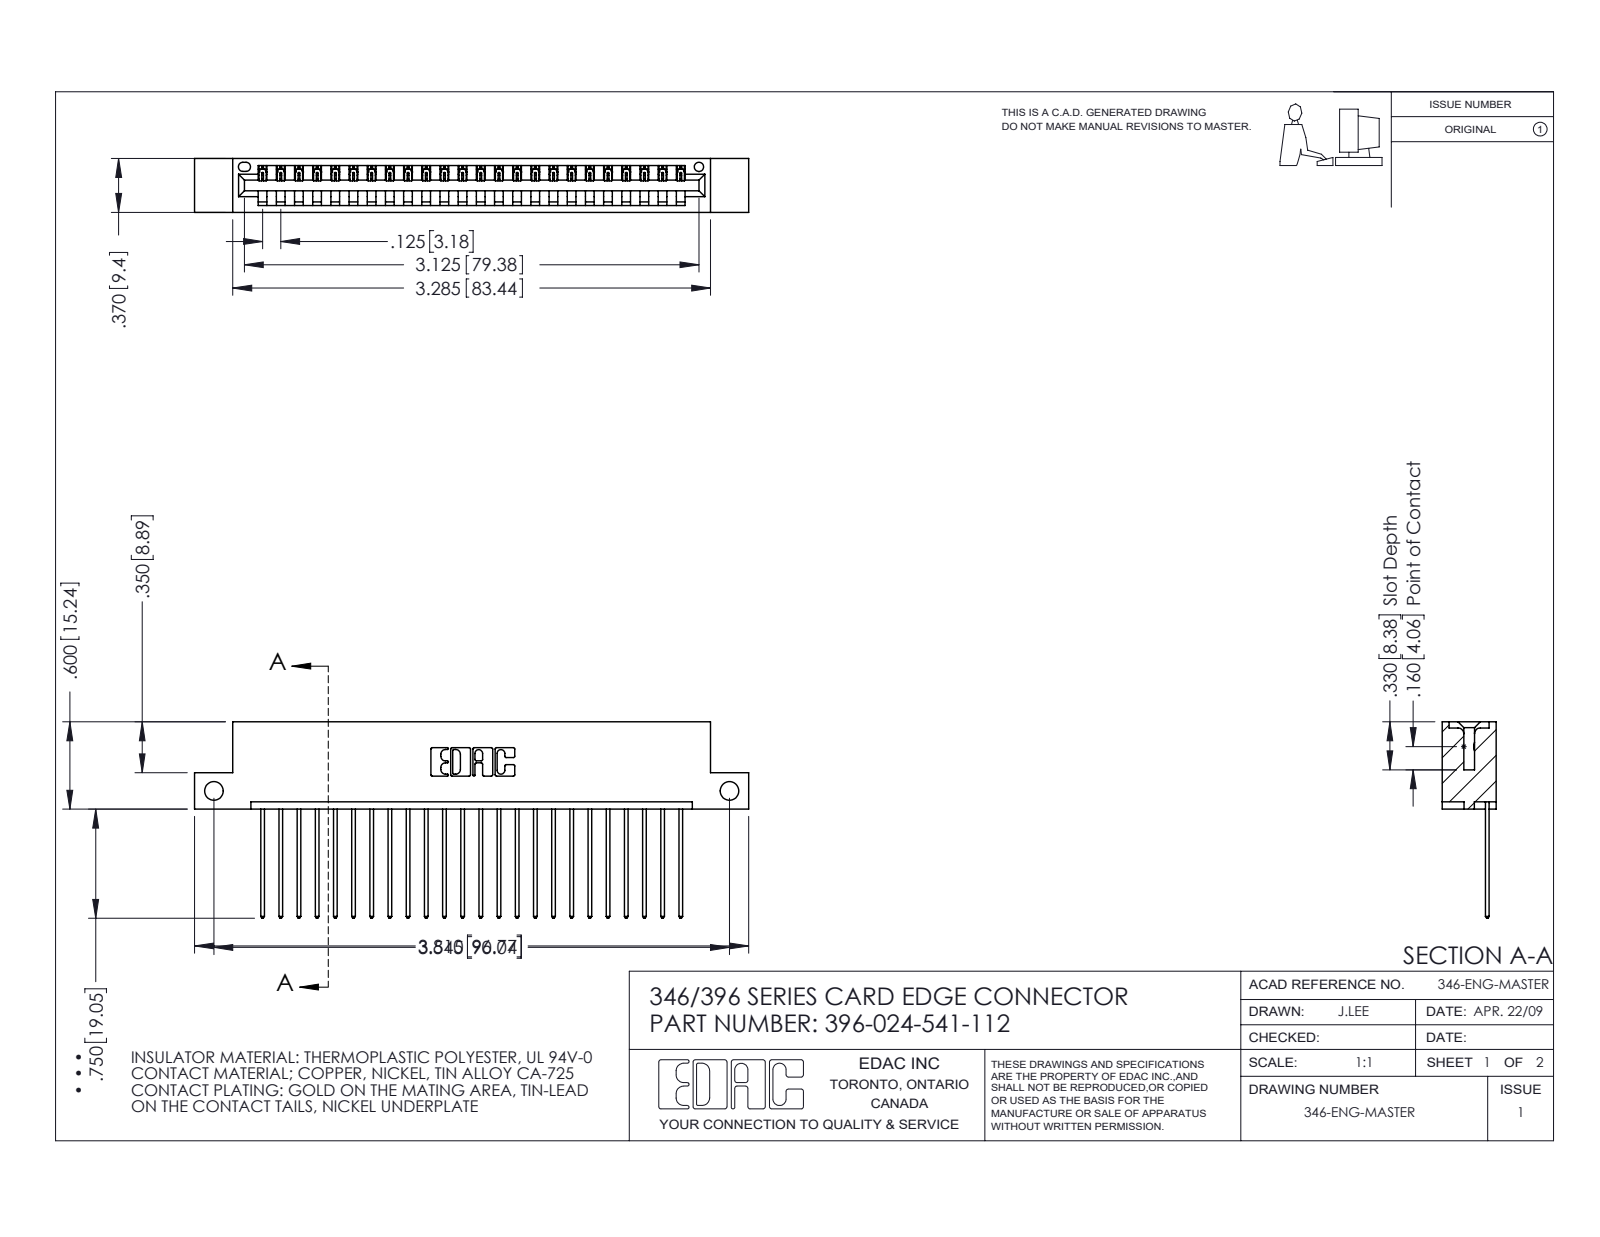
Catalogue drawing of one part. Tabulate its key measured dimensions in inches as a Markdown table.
| quantity | value |
| --- | --- |
| part name | 396-024-541-112; 345-292-001_345-293-141; 346 Part_Flush Mounting Lugs - Side Mount |
| STEP written by | SolidWorks 2016 (CONFIG_CONTROL_DESIGN) |
| units | inches |
| bodies | 25 solids, 1514 faces (1036 planar, 478 cylindrical, 0 other) |
| overall size | 3.81 × 1.35 × 0.37 |
| volume | 0.557 in³ |
| surface area | 17.9 in² |
| round holes (diameter × count) | 0.128 × 2, 0.064 × 1 |
| partial cylindrical surfaces (radius × count) | 0.006 × 48, 0.01 × 48, 0.01 × 22, 0.007 × 6, 0.031 × 6, 0.026 × 3, 0.031 × 2, 0.04 × 2 |
| main face-to-face distances | 0.048, 0.322, 0.25, 0.37, 0.072, 0.298, 0.025, 0.148, 0.222, 0.1 |
| hole center spacings | 3.545 |
